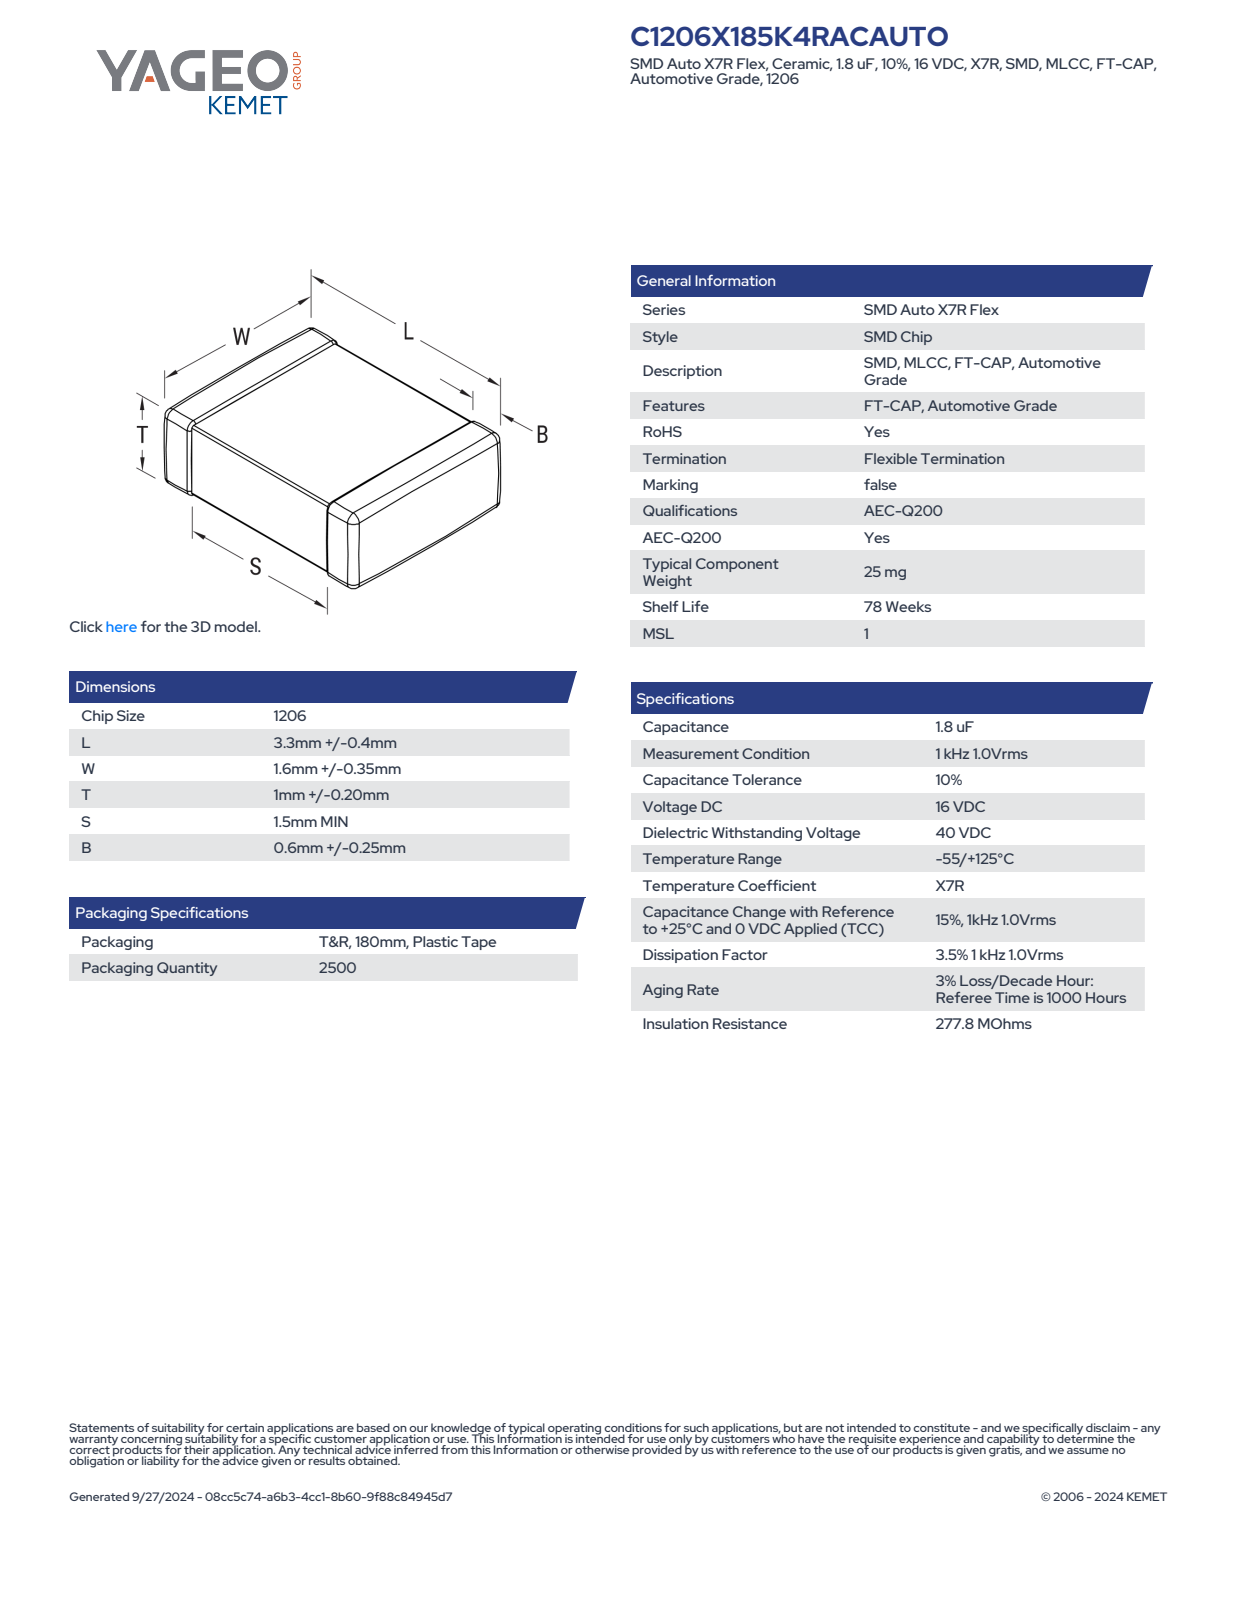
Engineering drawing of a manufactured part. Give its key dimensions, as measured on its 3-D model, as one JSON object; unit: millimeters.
{"part_name": "CCS_CCSTD_1206_L3.7W1.95T1.2B0.6", "step_written_by": "SolidWorks 2014 (AUTOMOTIVE_DESIGN)", "units": "millimeters", "bodies": {"solids": 4, "faces": 125, "planar": 71, "cylindrical": 38, "other": 16}, "overall_size": [3.7, 1.95, 1.2], "volume_mm3": 8, "surface_area_mm2": 28, "face_to_face_distances": [1.12, 1.16, 1.87, 1.91, 3.7, 1.2, 1.95, 1.71, 1.99, 2]}
